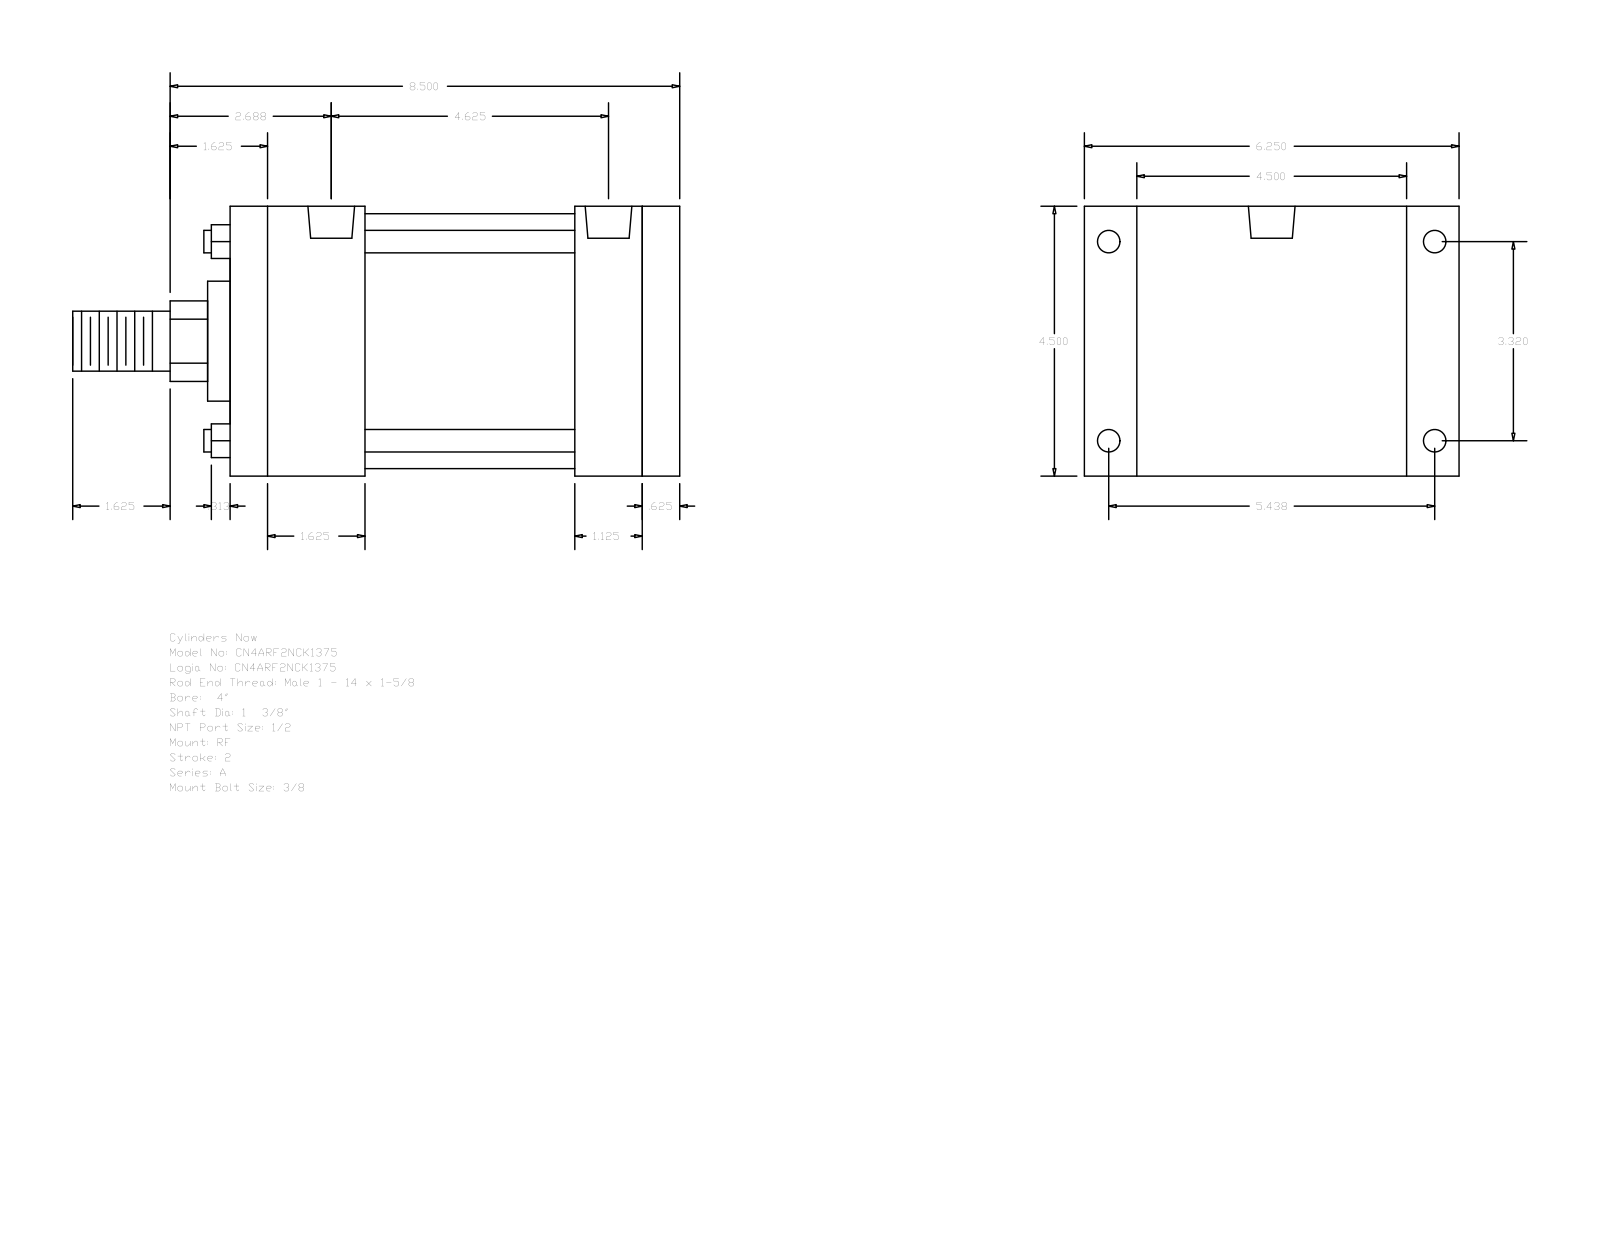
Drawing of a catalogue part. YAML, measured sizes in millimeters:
part_name: "A_RF__0400_1.375"
step_written_by: "GSSL Pune (CONFIG_CONTROL_DESIGN)"
units: millimeters
bodies: {solids: 0, faces: 92, planar: 64, cylindrical: 28, other: 0}
overall_size: [257.18, 158.75, 114.3]
round_holes:
  - {diameter: 8.73, count: 4}
  - {diameter: 9.53, count: 4}
  - {diameter: 19.77, count: 2}
round_bosses_or_shafts:
  - {diameter: 9.53, count: 4}
  - {diameter: 107.95, count: 1}
  - {diameter: 50.8, count: 1}
  - {diameter: 34.92, count: 1}
  - {diameter: 25.4, count: 1}
partial_cylinders:
  - {radius: 17.06, count: 1}
face_to_face_distances: [114.3, 190.5, 174.63, 15.87, 57.15, 28.58, 22.23, 136.53, 146.05, 44.45]
hole_center_spacings: [3.18, 84.32, 111.12, 114.3, 138.12, 161.82, 117.48]
